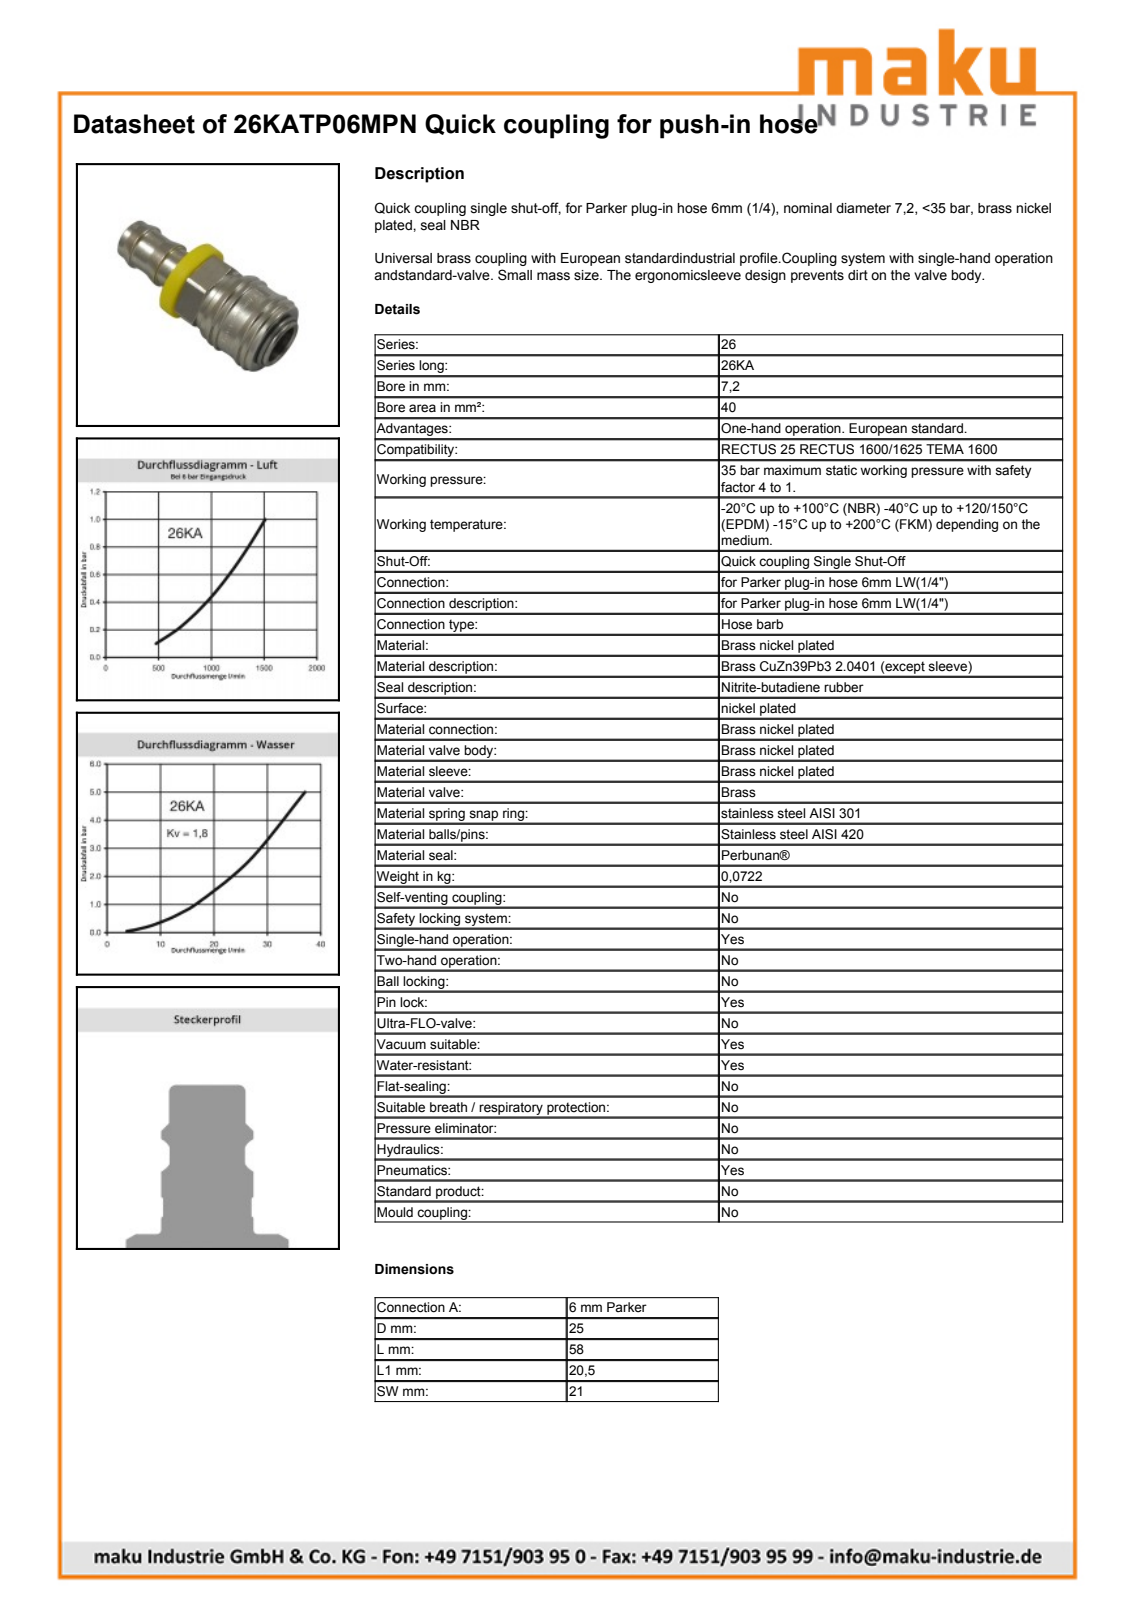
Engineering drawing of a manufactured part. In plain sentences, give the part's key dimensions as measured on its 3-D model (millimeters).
The part is named "D105984". Its 3-D file was written by "Autodesk Inventor 2011 (AUTOMOTIVE_DESIGN)". It is 2 solids with 480 faces: 180 planar, 68 cylindrical and 232 other. Overall it measures 53.1 by 24.8 by 24.8 millimeters. Its volume is 12 229 cubic millimeters and its surface area 7 867 square millimeters. Round holes: 1 of diameter 8.1, 1 of diameter 15, 1 of diameter 15.45, 1 of diameter 16.1, 1 of diameter 17, 1 of diameter 21.1. Round bosses or shafts: 1 of diameter 23.3, 1 of diameter 21, 1 of diameter 18, 1 of diameter 17.4, 1 of diameter 16.65, 1 of diameter 15.95, 1 of diameter 14.95, 1 of diameter 13.68. Partial cylindrical surfaces (rounded edges, fillets, slot ends): 1 of radius 11.55, 1 of radius 11.85. The main face-to-face distances are 21, 2.65, 1.2, 33.9, 31.25, 32.7, 30.05, 18.35, 11.7, 12.9.
